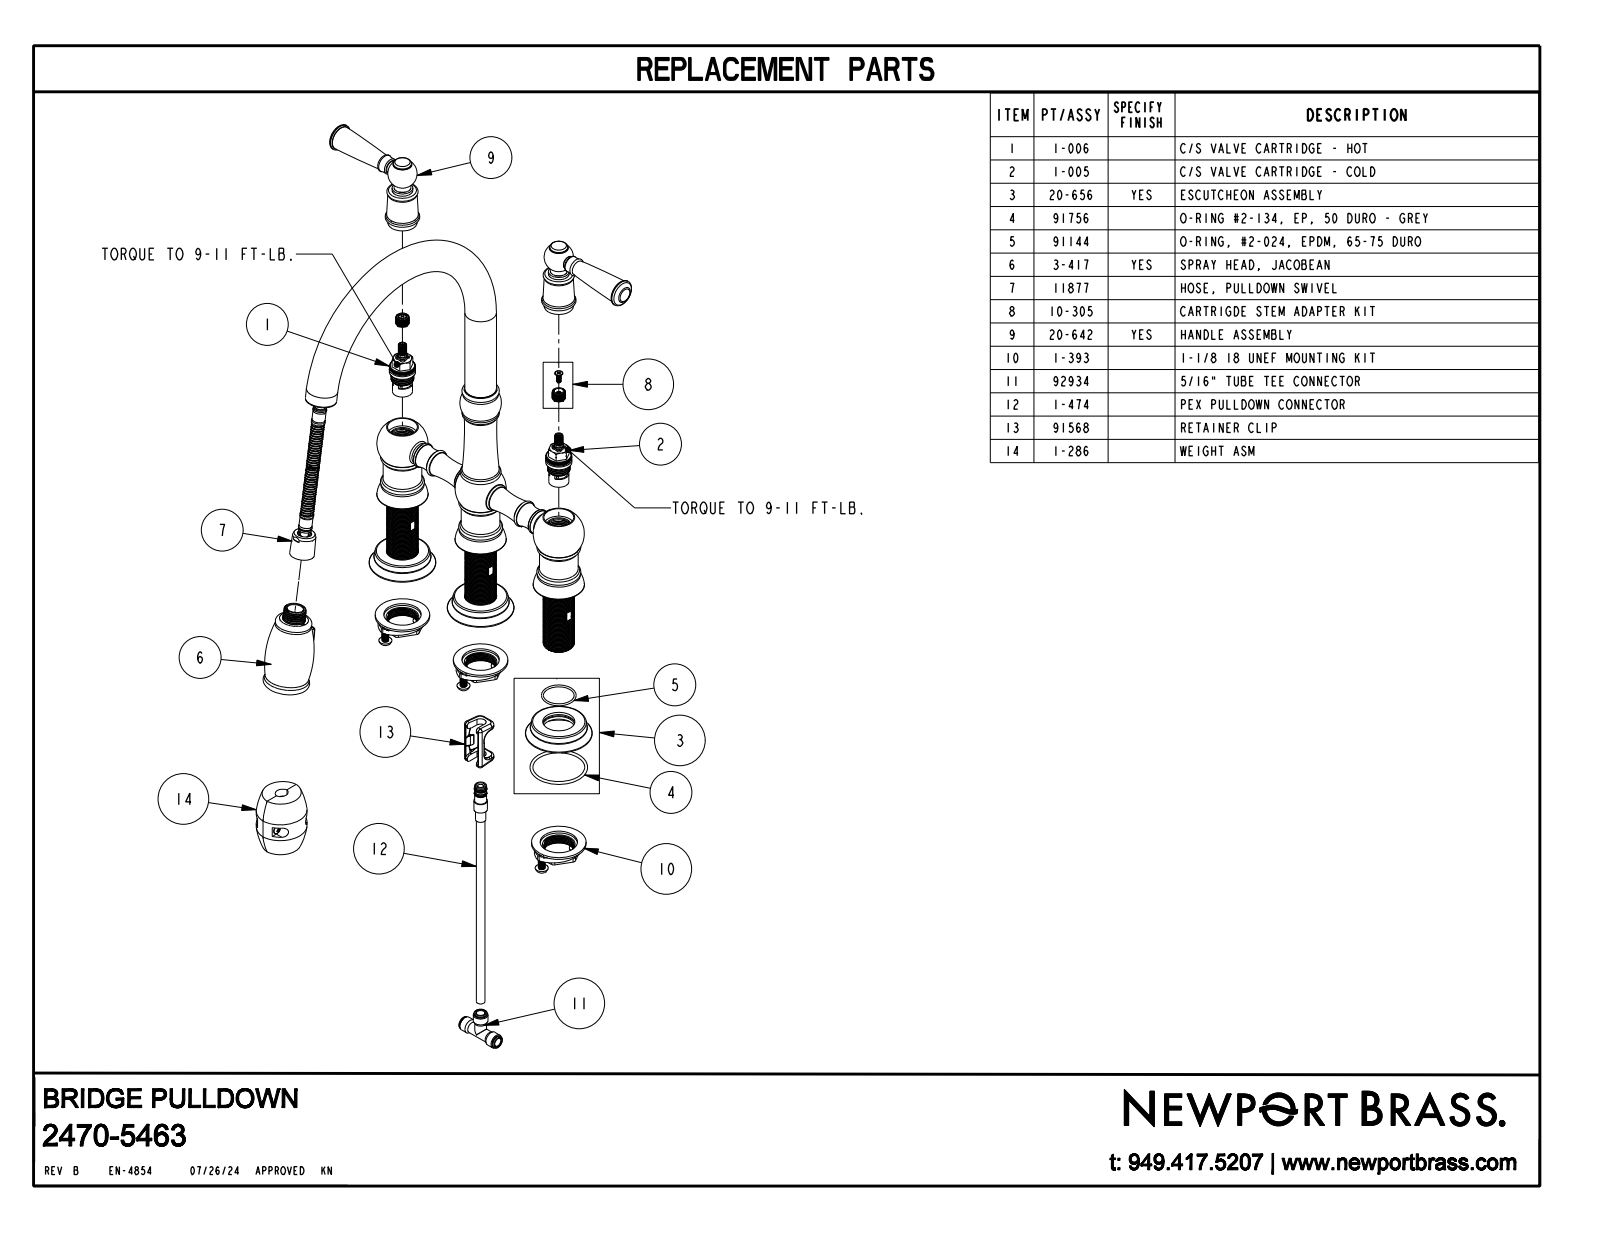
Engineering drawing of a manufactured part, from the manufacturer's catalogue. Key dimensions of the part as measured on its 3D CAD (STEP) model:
Part name (STEP PRODUCT): 2470-5463_SW0001
STEP written by: CREO PARAMETRIC BY PTC INC, 2018400 (CONFIG_CONTROL_DESIGN)
Units: inches
Bodies: 1 solid, 451 faces (73 planar, 47 cylindrical, 331 other)
Overall size (bounding box): 15.265 × 14.772 × 10.607
Volume: 59.58 in³ · Surface area: 211.5 in²
Round bosses / shafts (diameter × count): ⌀1.4 ×3, ⌀0.75 ×2, ⌀0.65 ×2, ⌀0.615 ×2, ⌀0.51 ×2, ⌀1.14 ×1, ⌀1.124 ×1, ⌀0.983 ×1
Partial cylindrical surfaces — rounded edges, fillets, slot ends (radius × count): R0.059 ×4, R0.08 ×4, R0.098 ×2, R0.12 ×2, R0.105 ×1
Main face-to-face distances: 0.55, 4.785, 4.235, 4.885, 4.335, 0.1, 2.754, 2.75, 14.772, 4.906
